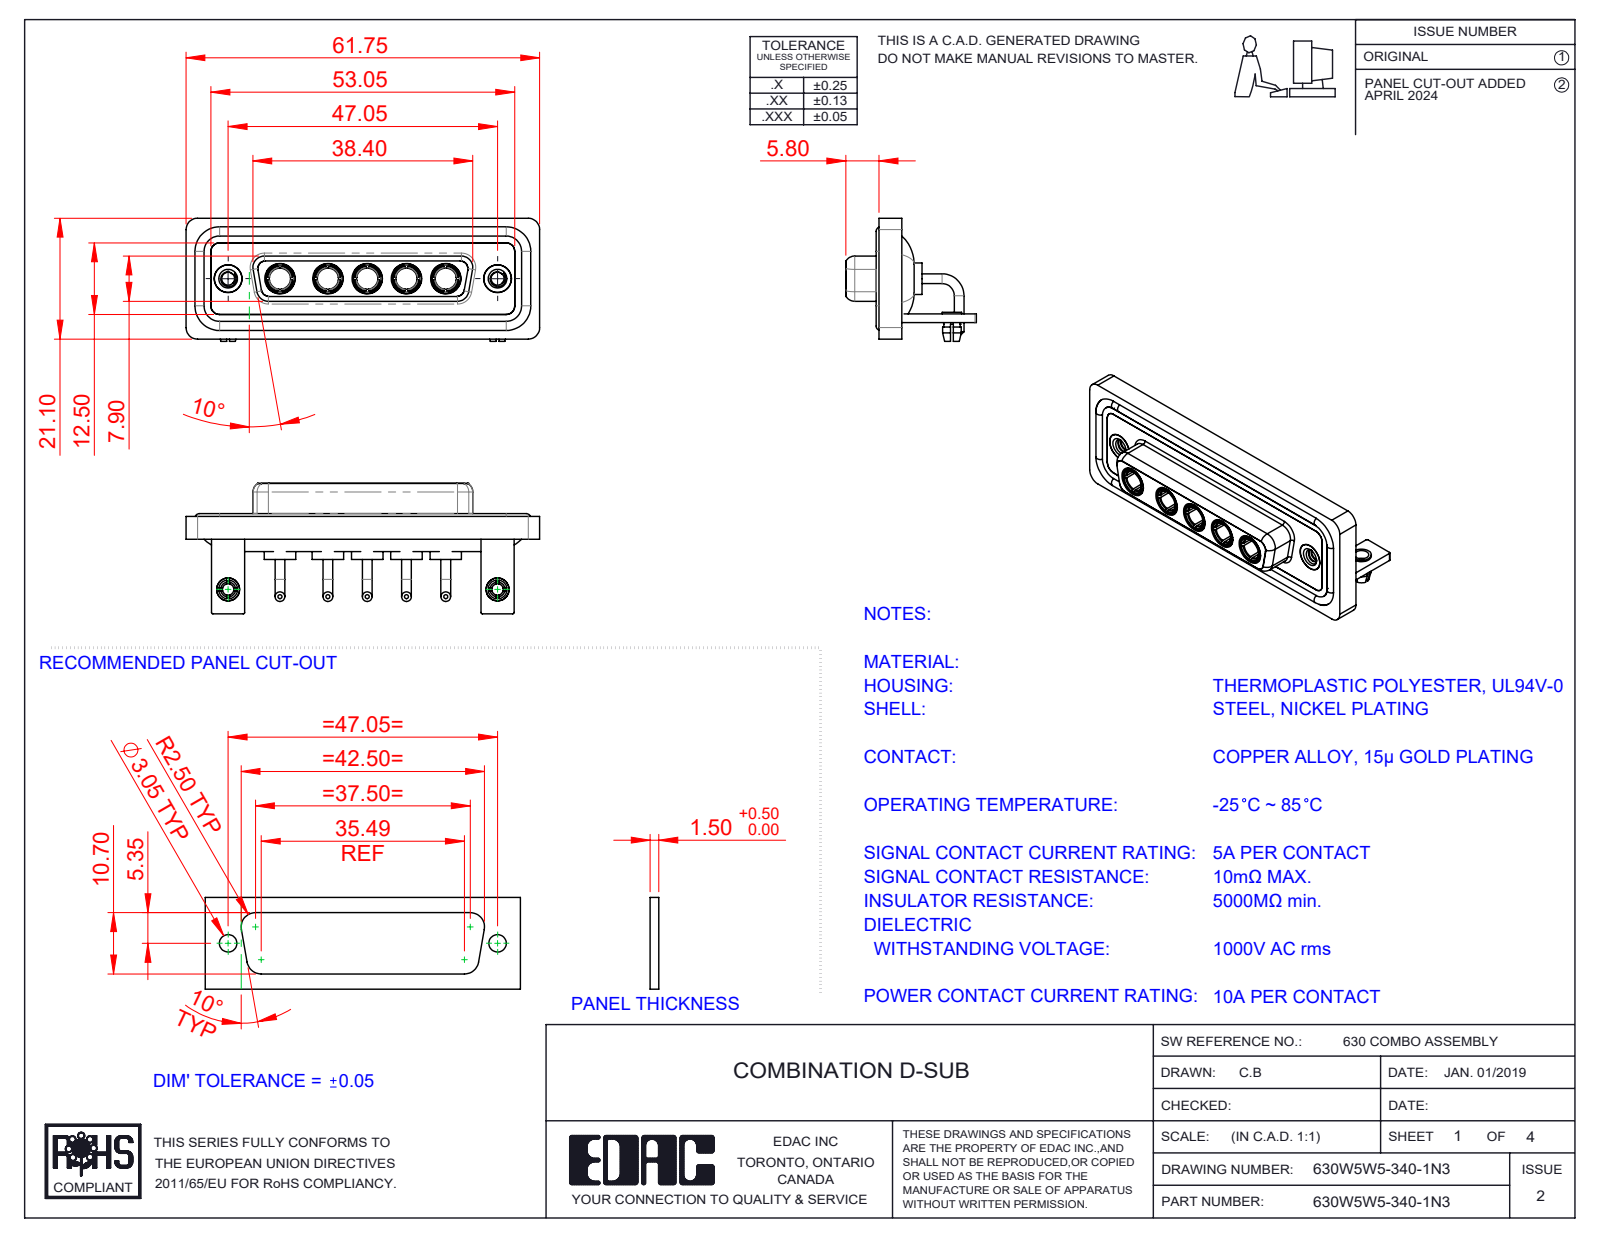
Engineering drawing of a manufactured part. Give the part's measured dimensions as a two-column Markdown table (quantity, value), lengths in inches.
| quantity | value |
| --- | --- |
| part name | 630Combo Board Lock_50 Contacts; 630Combo Threaded Rivet_2; 630Combo Shell Rear_25 Contacts; 630Combo Housing_5W5 (+5 more) |
| STEP written by | SolidWorks 2023 (CONFIG_CONTROL_DESIGN) |
| units | inches |
| bodies | 21 solids, 916 faces (318 planar, 369 cylindrical, 229 other) |
| overall size | 2.431 × 0.898 × 0.846 |
| volume | 0.522 in³ |
| surface area | 22.48 in² |
| round holes (diameter × count) | 0.191 × 7, 0.146 × 5, 0.209 × 5, 0.079 × 2, 0.089 × 2, 0.098 × 2, 0.126 × 2, 0.157 × 2, 0.159 × 2, 0.197 × 2 |
| round bosses / shafts (diameter × count) | 0.067 × 10, 0.217 × 5, 0.205 × 5, 0.195 × 5, 0.187 × 5, 0.148 × 5, 0.063 × 4, 0.195 × 2 |
| partial cylindrical surfaces (radius × count) | 0.079 × 19, 0.059 × 18, 0.01 × 16, 0.053 × 8, 0.063 × 8, 0.02 × 5, 0.083 × 5, 0.024 × 4 |
| main face-to-face distances | 0.016, 0.071, 0.059, 0.114, 0.146, 0.161, 0.043, 0.055, 0.063, 0.098 |
| hole center spacings | 0.27, 0.356, 1.496, 1.852, 0.27, 0.33, 0.54, 0.541 |
